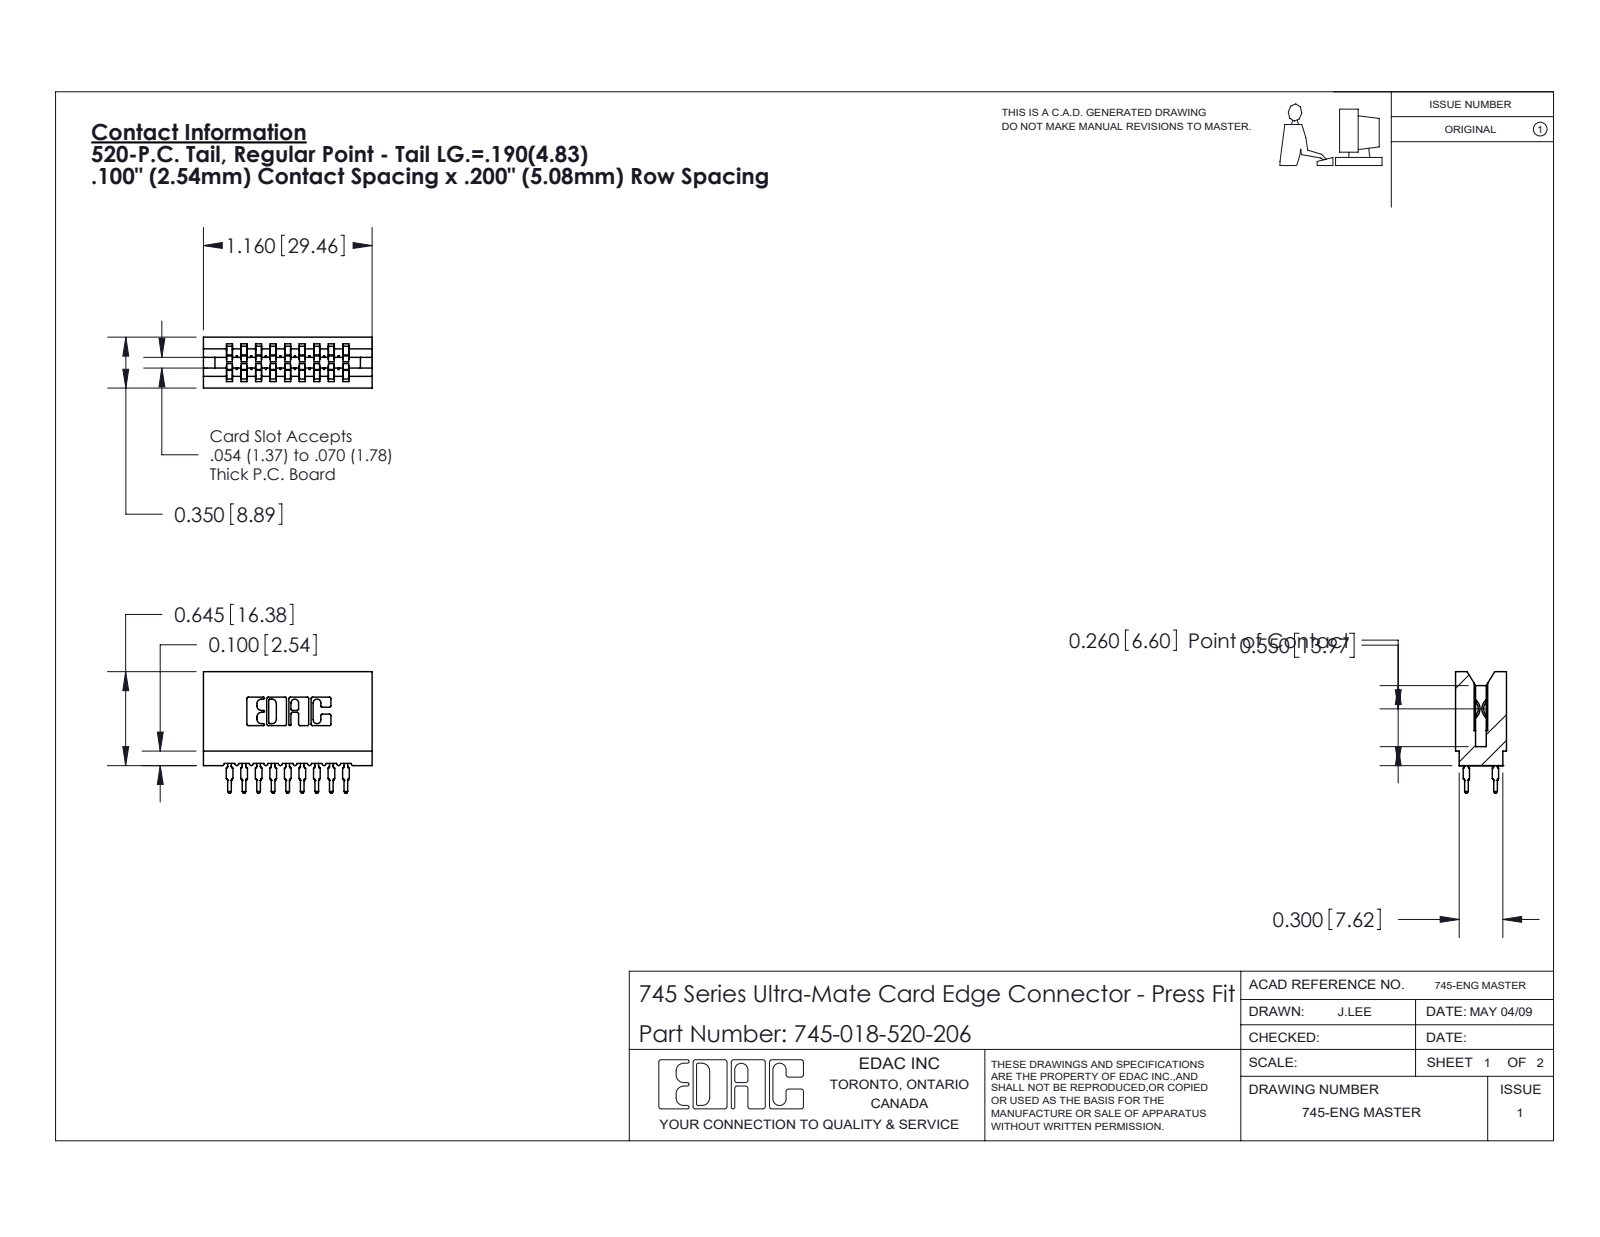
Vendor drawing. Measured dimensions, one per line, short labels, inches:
name: 745 Part_Insulator Option - 06; 745-018-520-206; 745-292-001_520
written by: SolidWorks 2020 (CONFIG_CONTROL_DESIGN)
unit: in
bodies: 19 solids, 1707 faces (884 planar, 355 cylindrical, 468 other)
size: 1.16 × 0.836 × 0.35
volume: 0.172 in³; area: 7.6 in²
rounds: 36× R0.021, 22× R0.01, 18× R0.015, 8× R0.005, 8× R0.011, 6× R0.007, 6× R0.031, 3× R0.026
face distances: 0.1, 0.2, 0.3, 0.4, 0.042, 0.142, 0.5, 0.058, 0.242, 0.158
